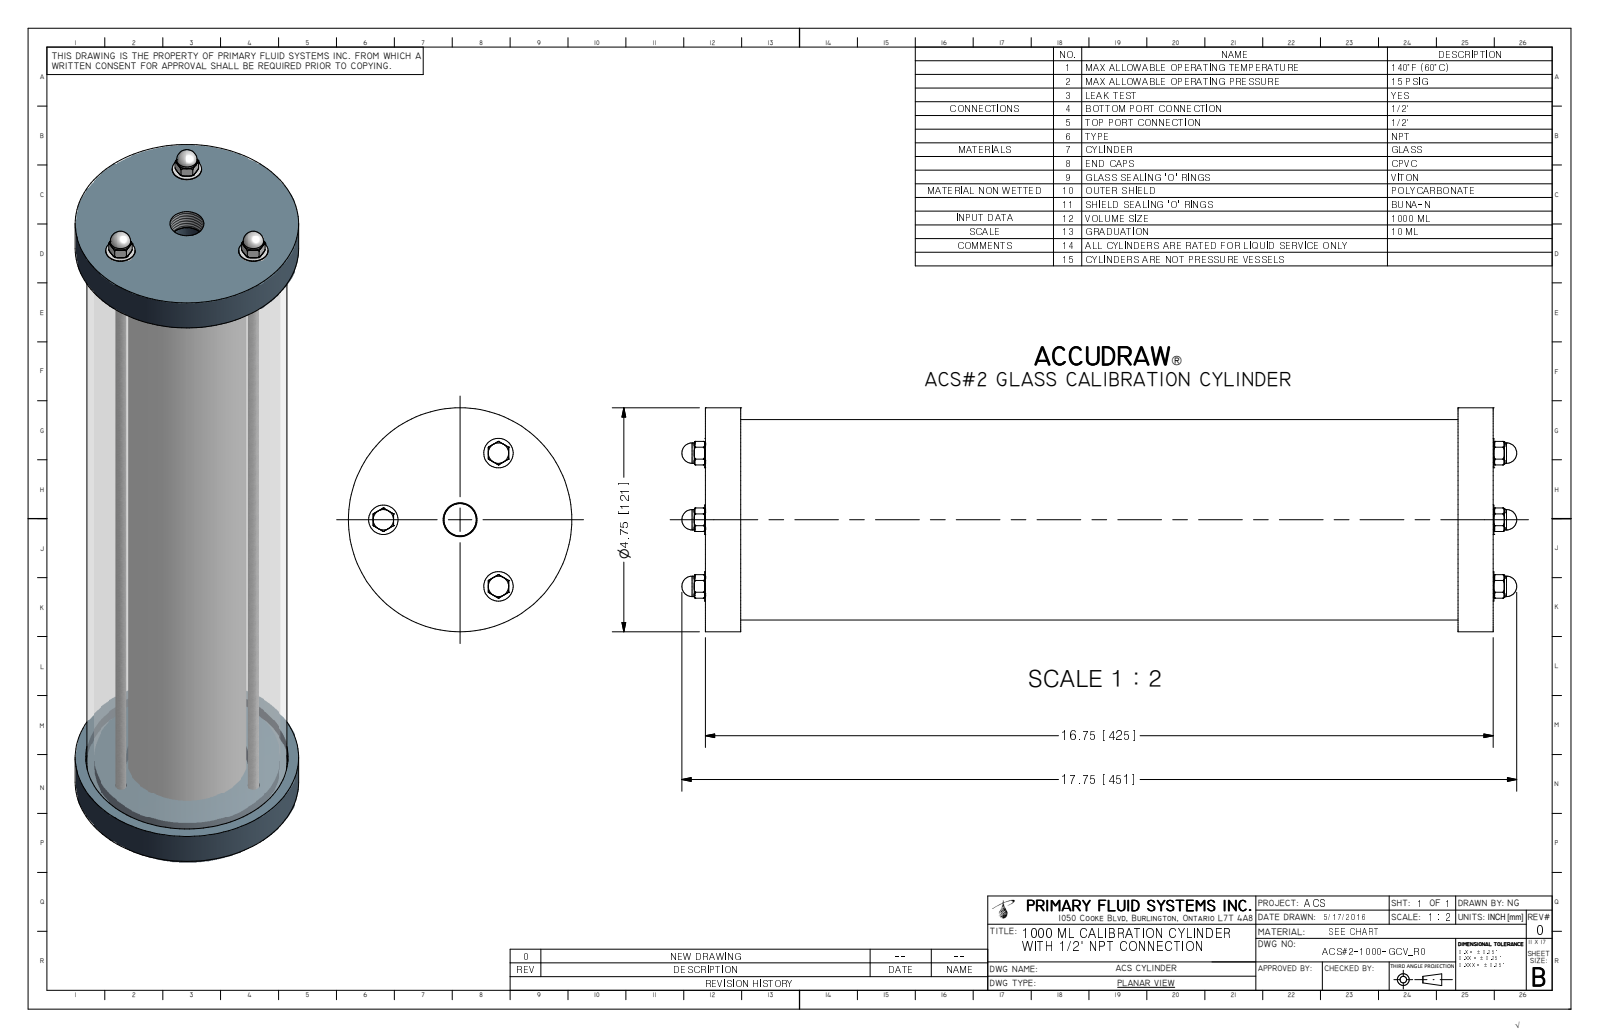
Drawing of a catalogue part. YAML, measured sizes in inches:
part_name: "ACS#2-1000-GCV_R0; ACS-3-1000-POLY_R3; ACS-2-1000-PC_R6; ACS-1-1000-A_R0 (+3 more)"
step_written_by: "Autodesk Inventor 2009 (AUTOMOTIVE_DESIGN)"
units: inches
bodies: {solids: 19, faces: 429, planar: 38, cylindrical: 41, other: 350}
overall_size: [17.75, 4.75, 4.75]
volume: 62.66
surface_area: 822.5
round_holes:
  - {diameter: 0.18, count: 3}
  - {diameter: 0.266, count: 3}
  - {diameter: 0.281, count: 3}
  - {diameter: 2.331, count: 1}
  - {diameter: 2.6, count: 1}
  - {diameter: 4, count: 1}
  - {diameter: 4.3, count: 1}
round_bosses_or_shafts:
  - {diameter: 0.625, count: 3}
  - {diameter: 0.25, count: 3}
  - {diameter: 4.75, count: 1}
  - {diameter: 4.25, count: 1}
  - {diameter: 3.95, count: 1}
  - {diameter: 2.519, count: 1}
  - {diameter: 2.2, count: 1}
face_to_face_distances: [16, 0.75, 16.75, 15.25, 0.475, 16.275, 0.275, 15.525, 0.375, 0.375]
hole_center_spacings: [1.631, 2.826]
